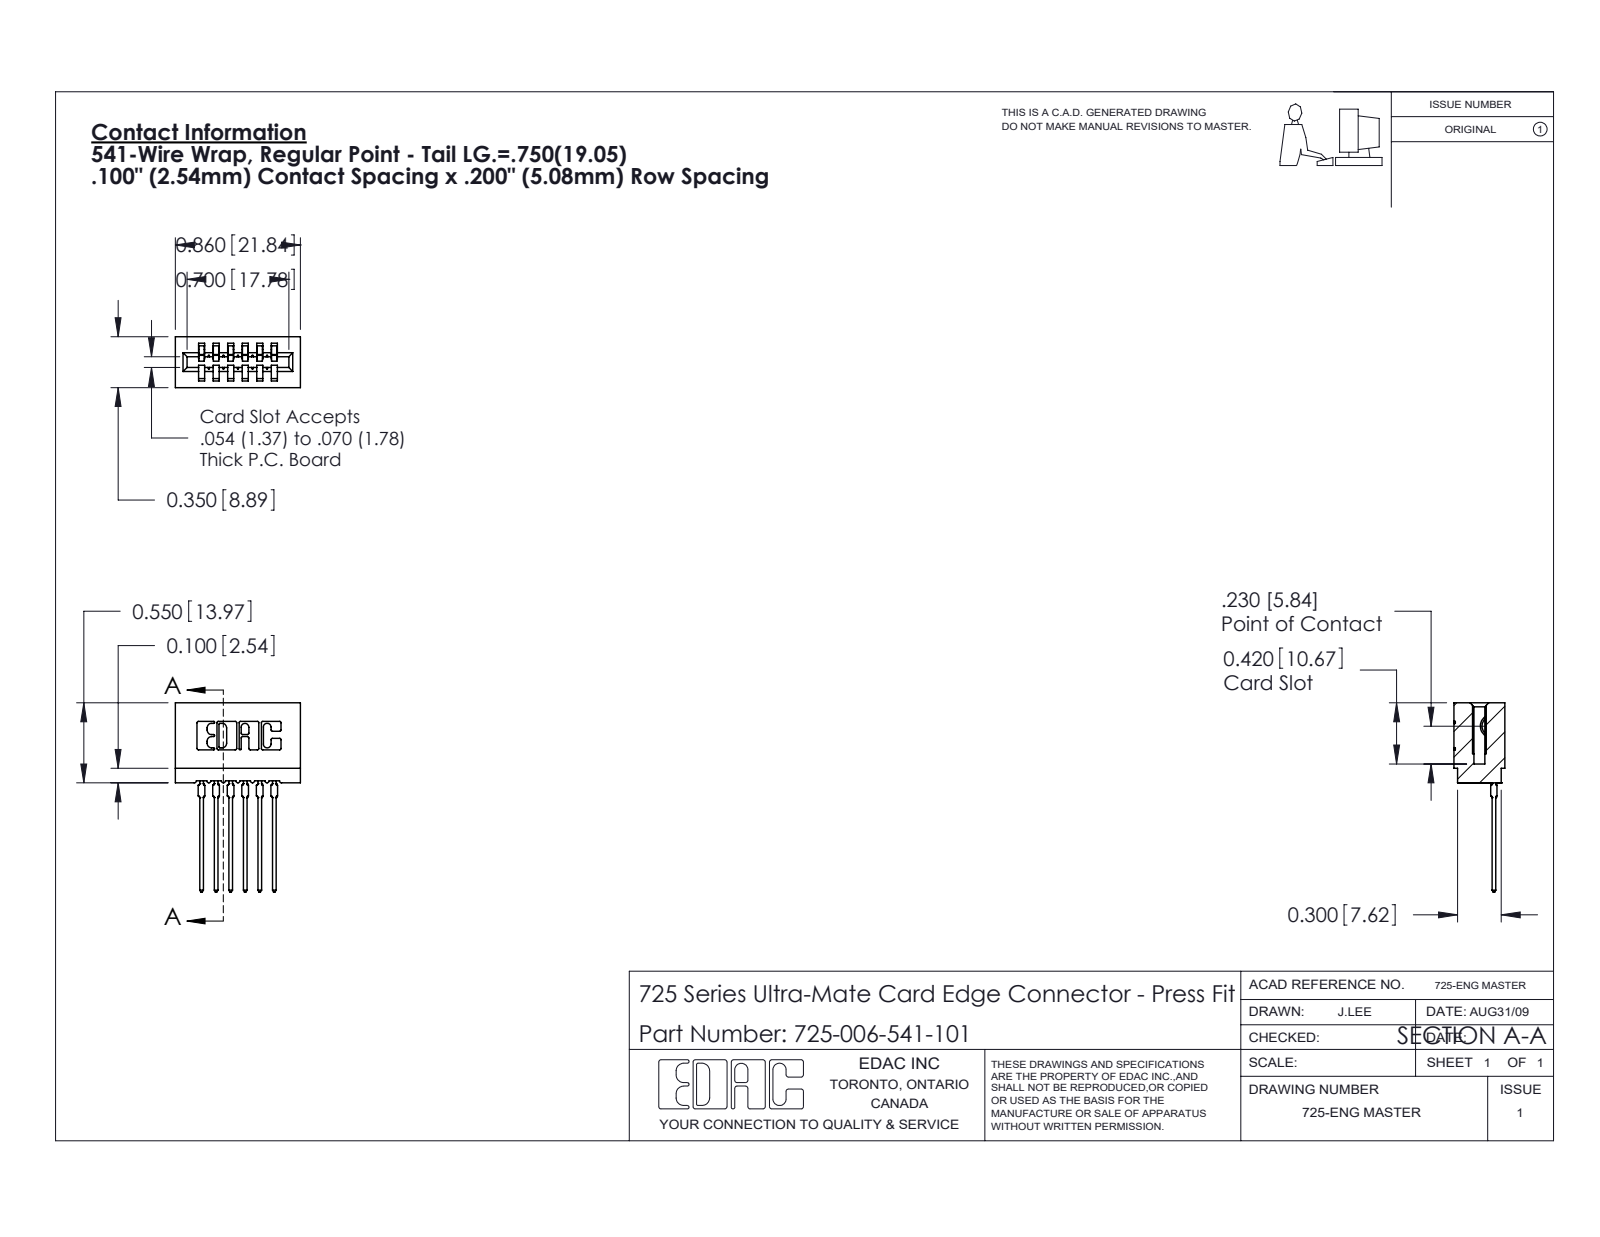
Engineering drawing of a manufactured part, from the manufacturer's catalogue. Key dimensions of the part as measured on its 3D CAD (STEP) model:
Part name (STEP PRODUCT): 725 Part_Insulator Option - 01; 725-006-541-101; 745-292-001_541
STEP written by: SolidWorks 2020 (CONFIG_CONTROL_DESIGN)
Units: inches
Bodies: 7 solids, 767 faces (457 planar, 154 cylindrical, 156 other)
Overall size (bounding box): 1.301 × 0.86 × 0.35
Volume: 0.115 in³ · Surface area: 4.791 in²
Partial cylindrical surfaces — rounded edges, fillets, slot ends (radius × count): R0.01 ×22, R0.015 ×12, R0.021 ×12, R0.007 ×6, R0.031 ×6, R0.005 ×4, R0.011 ×4, R0.026 ×3
Main face-to-face distances: 0.1, 0.2, 0.3, 0.042, 0.142, 0.058, 0.4, 0.242, 0.158, 0.35
